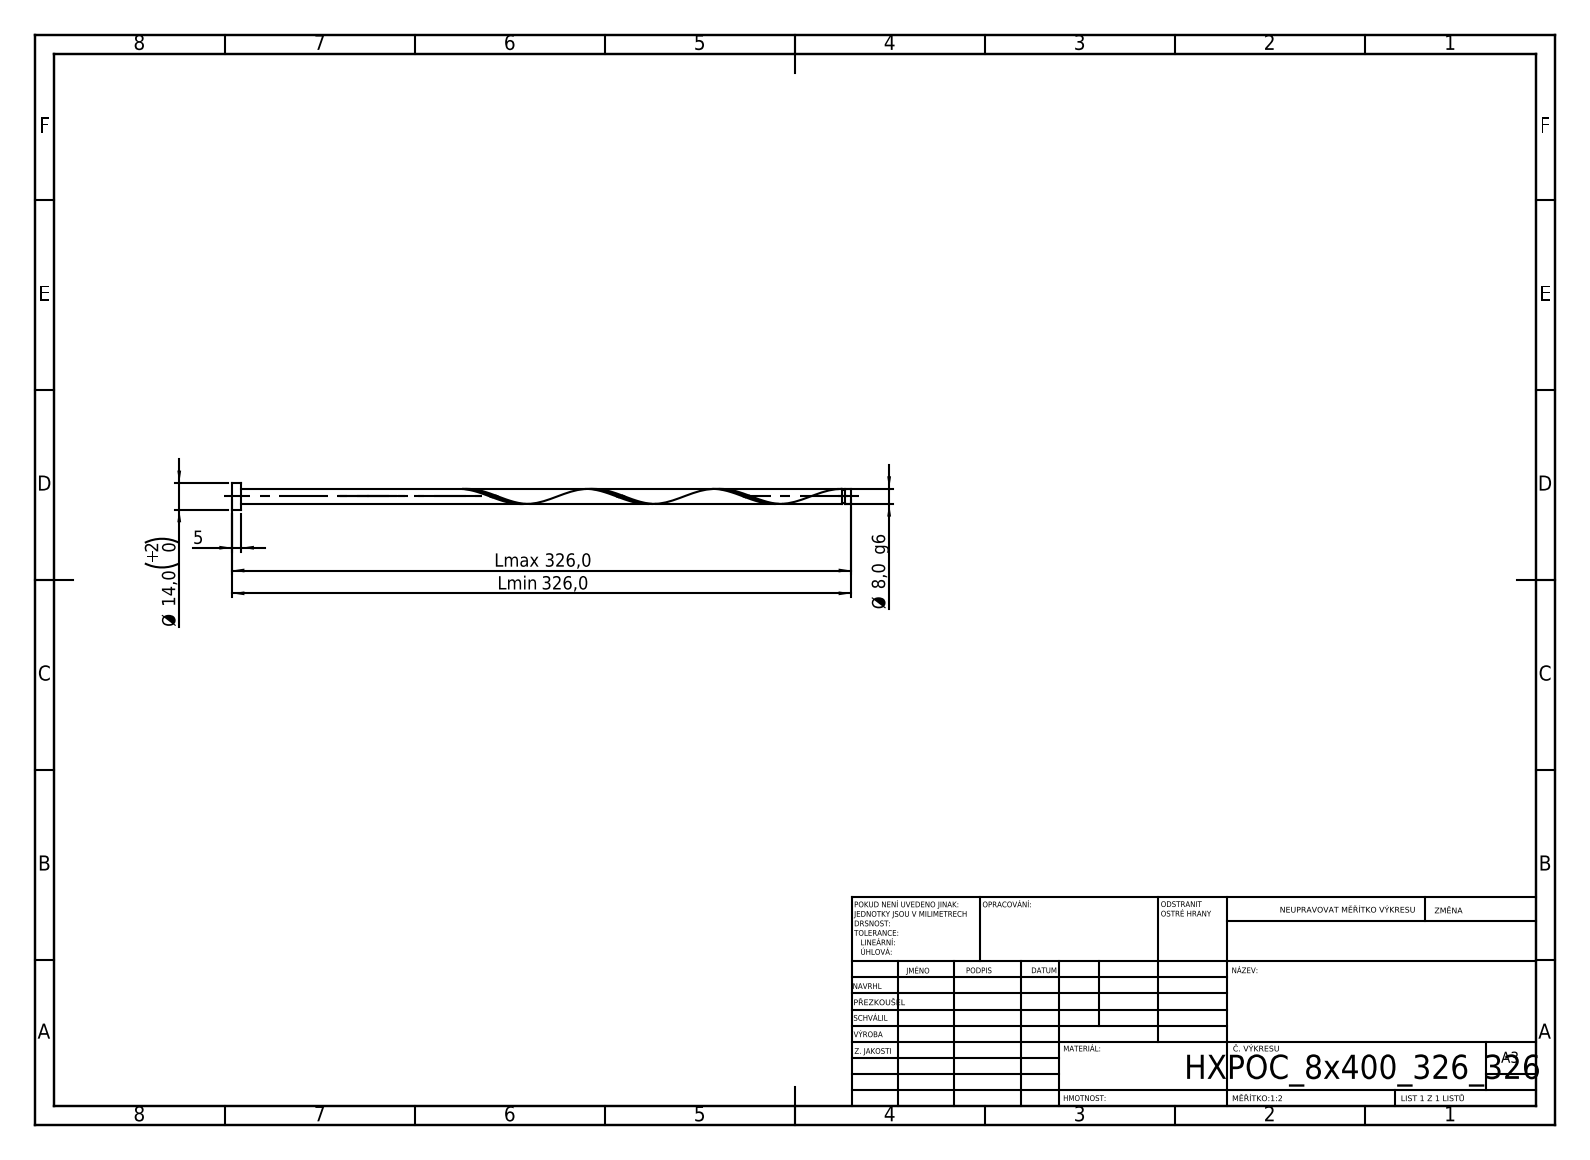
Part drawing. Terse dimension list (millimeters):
written by: SolidWorks 2019 (CONFIG_CONTROL_DESIGN)
unit: mm
bodies: 1 solid, 21 faces (6 planar, 14 cylindrical, 1 other)
size: 326 × 14 × 14
volume: 16 683 mm³; area: 8 789 mm²
bosses: 1× ⌀14, 1× ⌀8, 1× ⌀6.4
face distances: 5, 326, 321, 322.91, 317.91, 3.09, 321.31, 316.31, 1.6, 4.69
